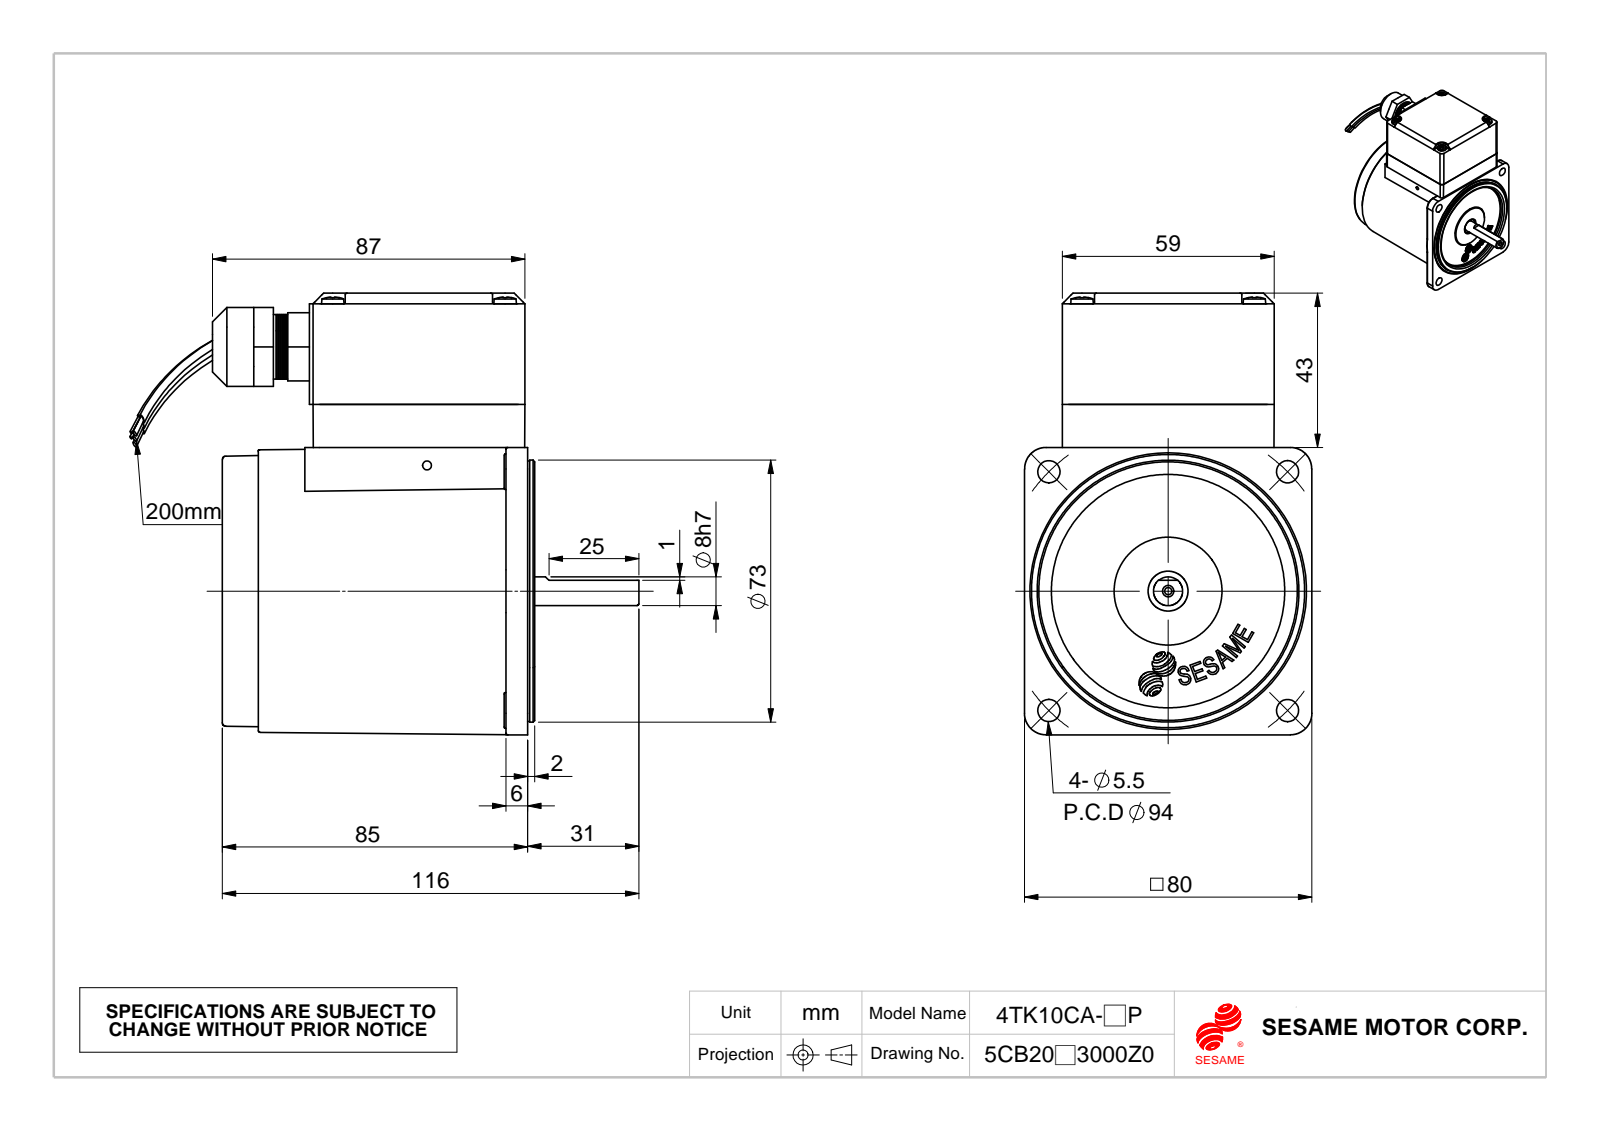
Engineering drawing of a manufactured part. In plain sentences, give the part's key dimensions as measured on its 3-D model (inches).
The part is named "M425TsA_成品; Ts下墊片; C475-C473_C475成品-車工; 25A_3.研磨 (+1 more)". Its 3-D file was written by "SolidWorks 2010 (CONFIG_CONTROL_DESIGN)". It is 14 solids with 2664 faces: 285 planar, 931 cylindrical and 1448 other. Overall it measures 5.58 by 4.843 by 3.15 inches. Its volume is 15.64 cubic inches and its surface area 158.8 square inches. Round holes: 4 of diameter 0.13, 4 of diameter 0.138, 4 of diameter 0.154, 4 of diameter 0.169, 4 of diameter 0.244, 2 of diameter 0.433, 1 of diameter 0.079, 1 of diameter 0.098, 1 of diameter 0.472, 1 of diameter 0.571, 1 of diameter 2.362, 1 of diameter 2.559. Round bosses or shafts: 4 of diameter 0.248, 4 of diameter 0.118, 1 of diameter 2.871, 1 of diameter 2.856, 1 of diameter 1.457, 1 of diameter 0.866, 1 of diameter 0.709, 1 of diameter 0.394. Partial cylindrical surfaces (rounded edges, fillets, slot ends): 12 of radius 0.02, 12 of radius 0.079, 8 of radius 0.024, 8 of radius 0.046, 8 of radius 0.051, 8 of radius 0.089, 6 of radius 0.157, 4 of radius 0.006. The main face-to-face distances are 0.472, 0.039, 0.059, 0.02, 0.118, 0.03, 3.307, 3.15, 3.268, 3.248. The hole center spacings are 1.85, 1.89, 2.617, 0.459, 0.486, 0.5, 0.981, 0.984.
